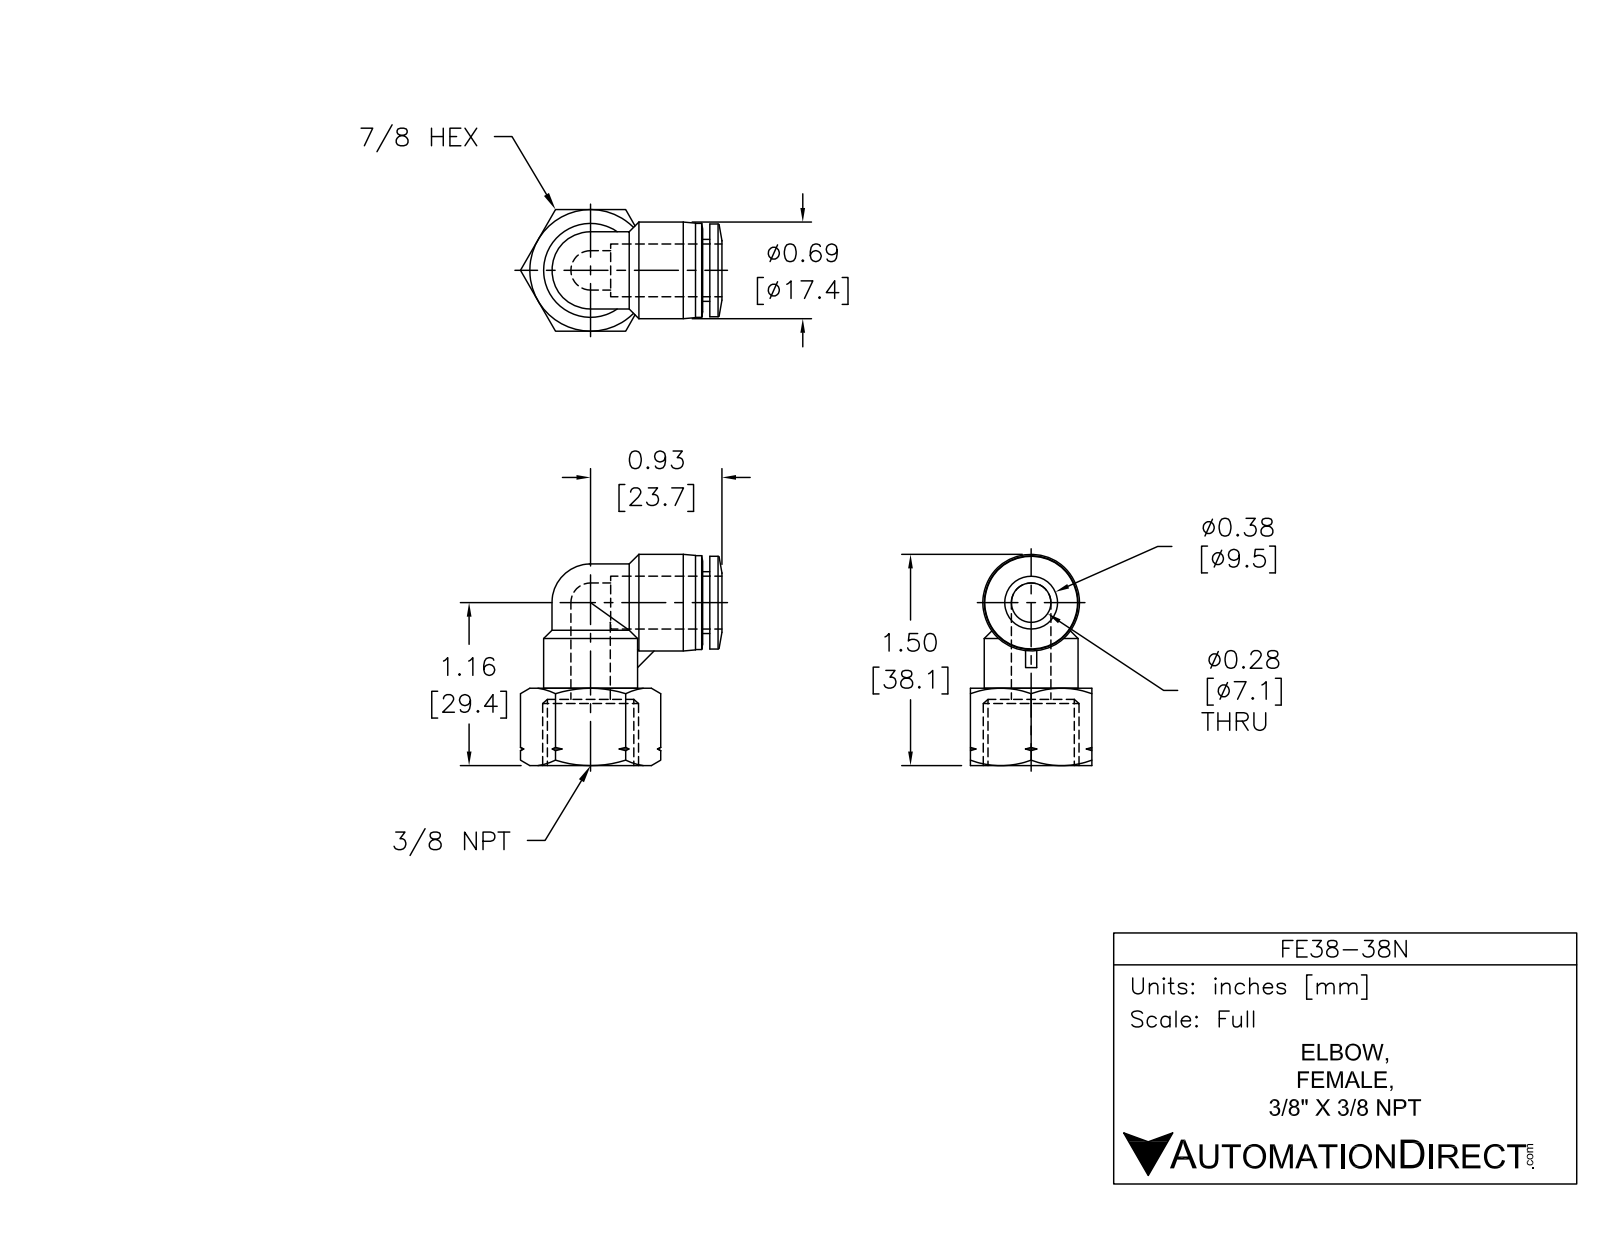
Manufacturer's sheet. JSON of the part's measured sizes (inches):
{"part_name": "FE38-38N", "step_written_by": "SolidWorks 2015 (AUTOMOTIVE_DESIGN)", "units": "inches", "bodies": {"solids": 1, "faces": 85, "planar": 16, "cylindrical": 20, "other": 49}, "overall_size": [1.506, 1.467, 0.866], "volume_in3": 0.534, "surface_area_in2": 8.833, "round_holes": [[0.276, 2], [0.386, 1]], "round_bosses_or_shafts": [[0.669, 2], [0.689, 1], [0.661, 1], [0.551, 1], [0.441, 1]], "partial_cylinders_radius": [[0.276, 1]], "face_to_face_distances": [0.866, 0.472, 0.079, 0.551, 0.051, 0.654, 0.705, 0.394, 0.602, 0.102]}
